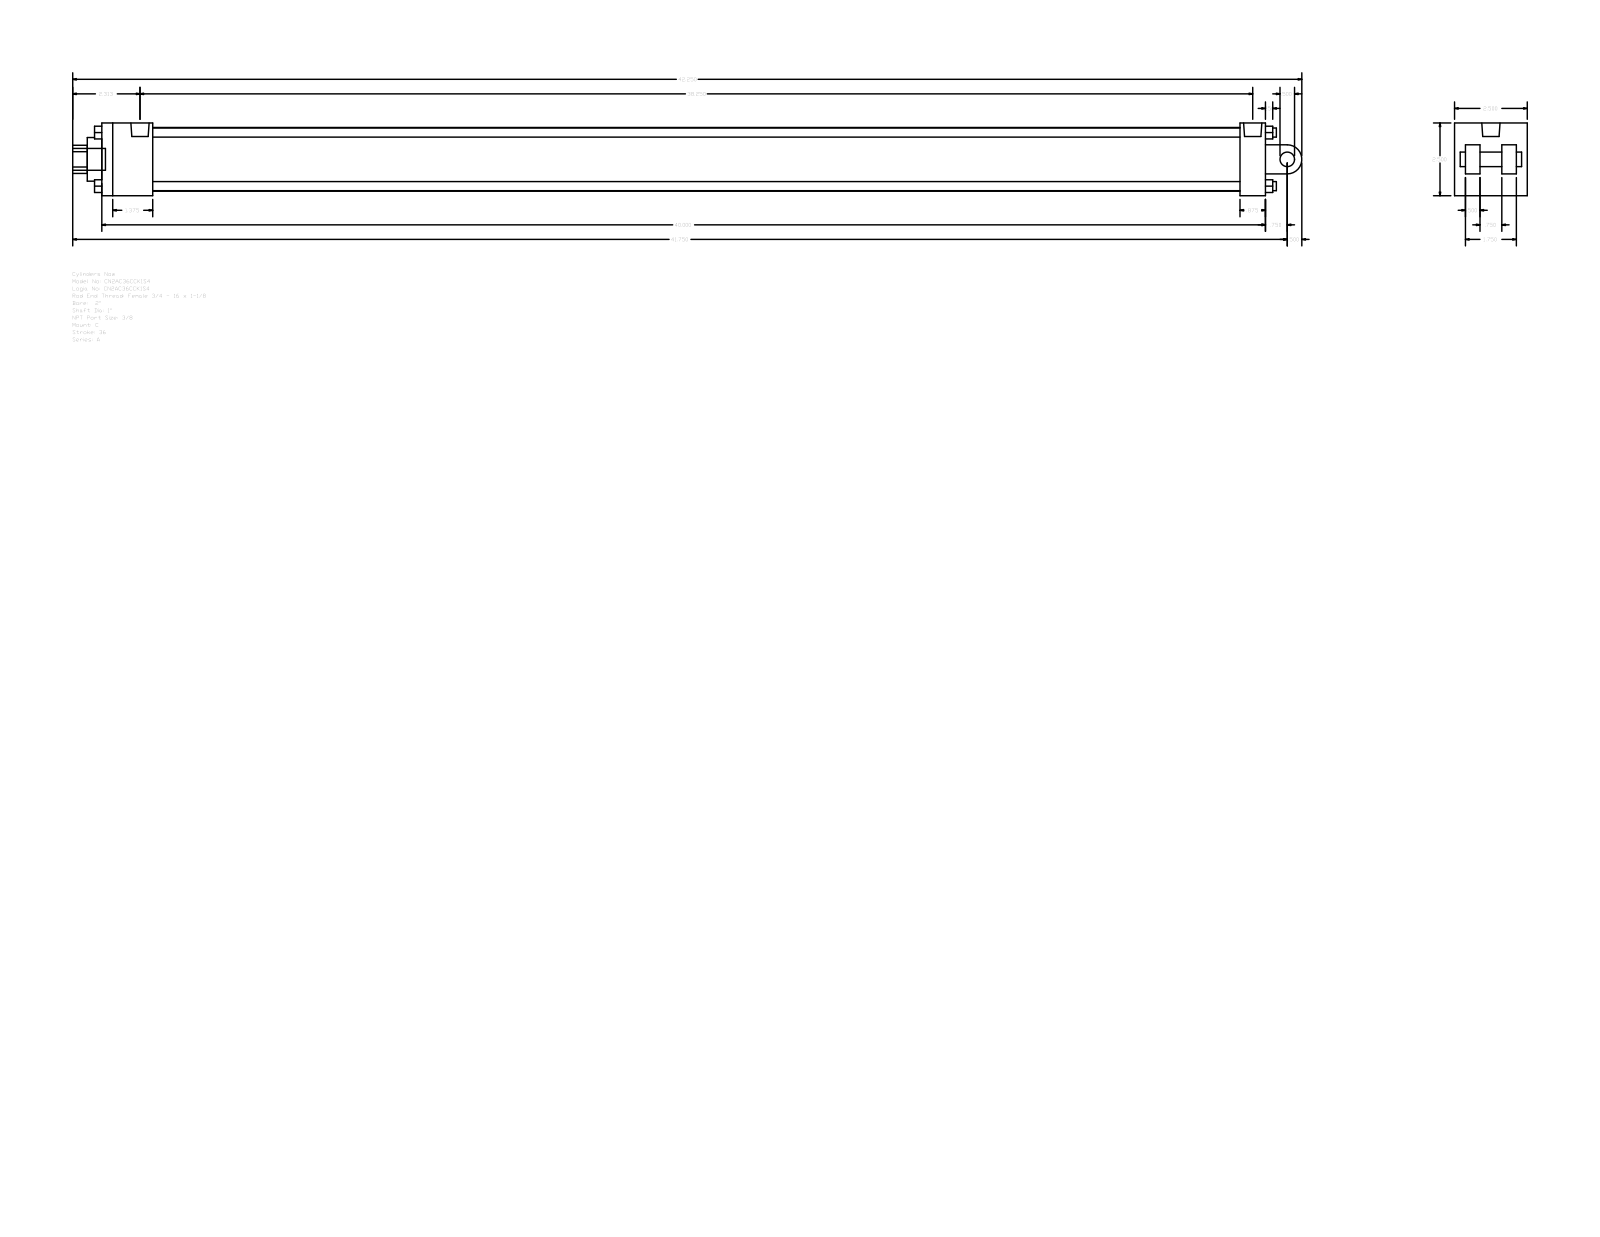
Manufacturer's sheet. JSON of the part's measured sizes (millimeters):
{"part_name": "A_C__0200_1", "step_written_by": "GSSL Pune (CONFIG_CONTROL_DESIGN)", "units": "millimeters", "bodies": {"solids": 0, "faces": 135, "planar": 102, "cylindrical": 33, "other": 0}, "overall_size": [1073.15, 63.5, 63.5], "round_holes": [[5.56, 2], [15.93, 1], [25.4, 1], [38.1, 1], [55.63, 1]], "round_bosses_or_shafts": [[7.94, 4], [5.56, 2], [19.05, 1], [15.93, 1], [12.7, 1]], "partial_cylinders_radius": [[12.29, 1], [12.7, 1]], "face_to_face_distances": [63.5, 1016, 44.45, 12.7, 9.52, 41.28, 971.55, 993.77, 949.32, 22.23], "hole_center_spacings": [3.98]}
